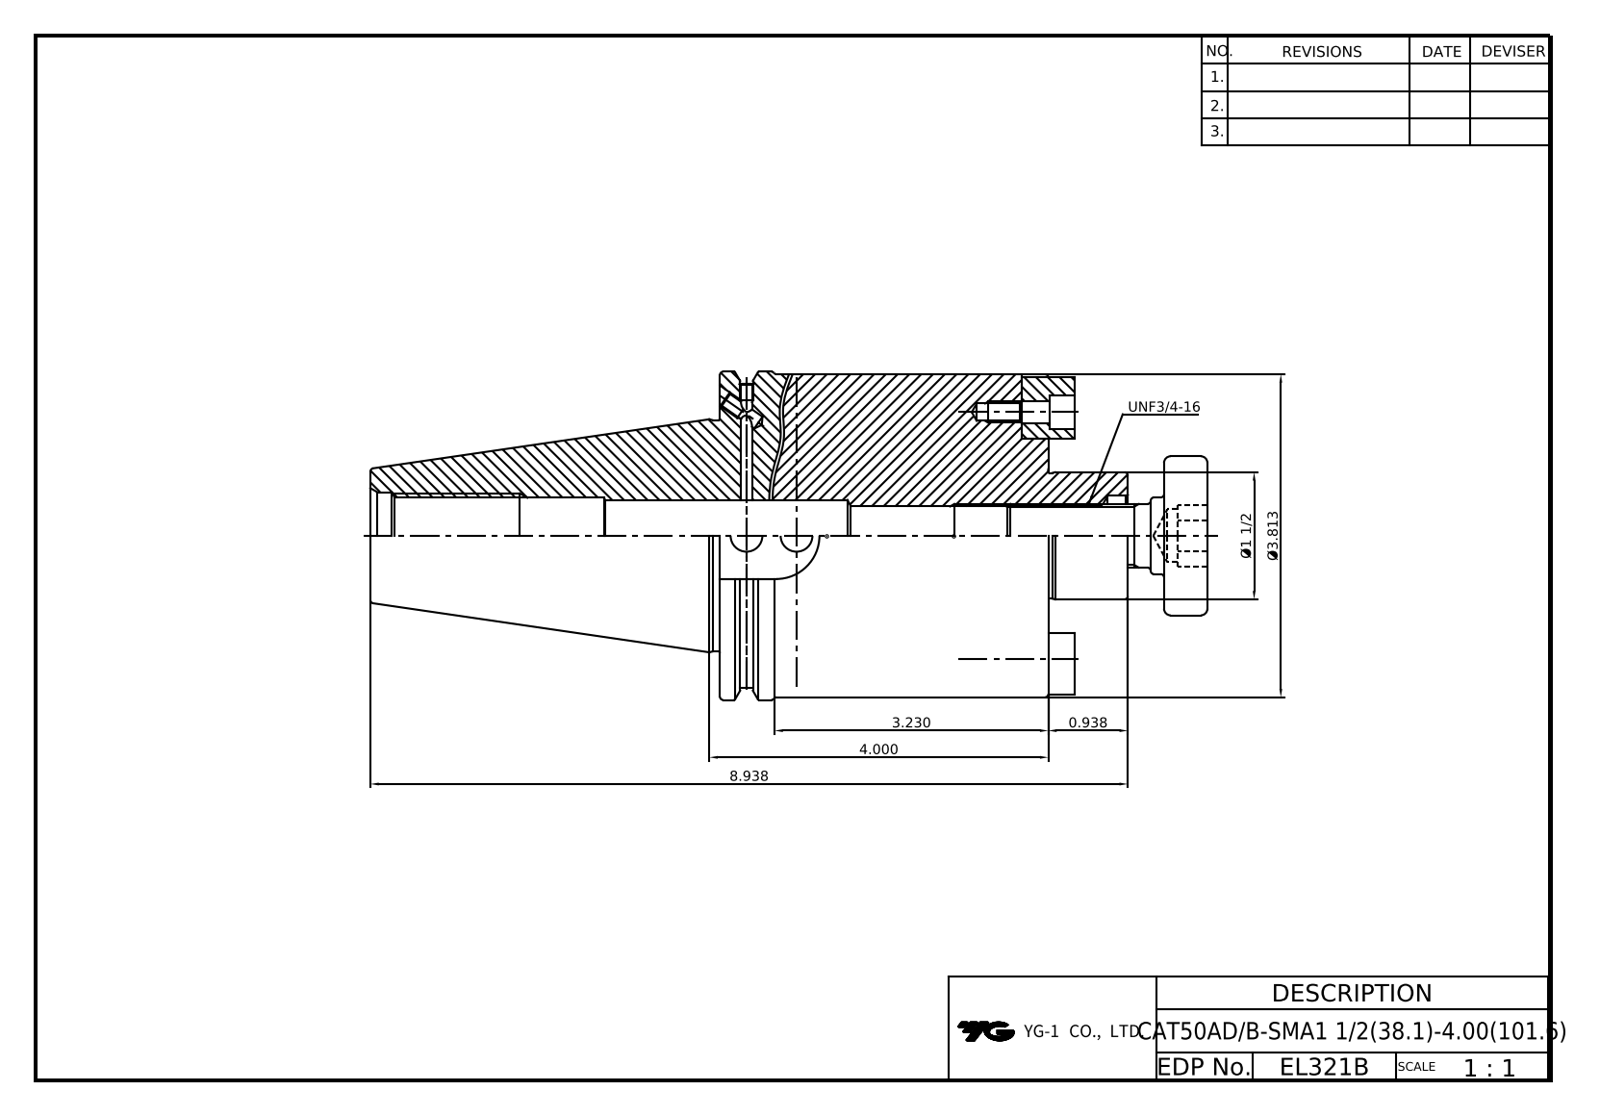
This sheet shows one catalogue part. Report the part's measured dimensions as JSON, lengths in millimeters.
{"part_name": "LO-CAT50ADB-SMA38.1-101; LO-CAT50ADB-SMA38.1-101.6; DRIVE KEY-15.875x15.875x18.5; COLLAR BOLT-UNF3_4-16x47L", "step_written_by": "Autodesk Inventor 2020 (AUTOMOTIVE_DESIGN)", "units": "millimeters", "bodies": {"solids": 4, "faces": 148, "planar": 65, "cylindrical": 45, "other": 38}, "overall_size": [240.03, 98.42, 96.85], "volume_mm3": 952181, "surface_area_mm2": 94379, "round_holes": [[3.24, 2], [4.13, 2], [4.2, 2], [4.98, 2], [5, 2], [6.6, 2], [9.53, 2], [10.3, 2], [15.88, 1], [17.32, 1], [21.5, 1], [21.97, 1]], "round_bosses_or_shafts": [[98.42, 1], [96.85, 1], [91.29, 1], [69.25, 1], [47.7, 1], [38.1, 1], [37.7, 1], [23, 1]], "partial_cylinders_radius": [[7.93, 2], [12.95, 1]], "face_to_face_distances": [98.43, 122.26, 23.83, 135.26, 36.83, 13, 90.36, 8.07, 31.9, 44.9], "hole_center_spacings": [37.06, 15, 74.12]}
